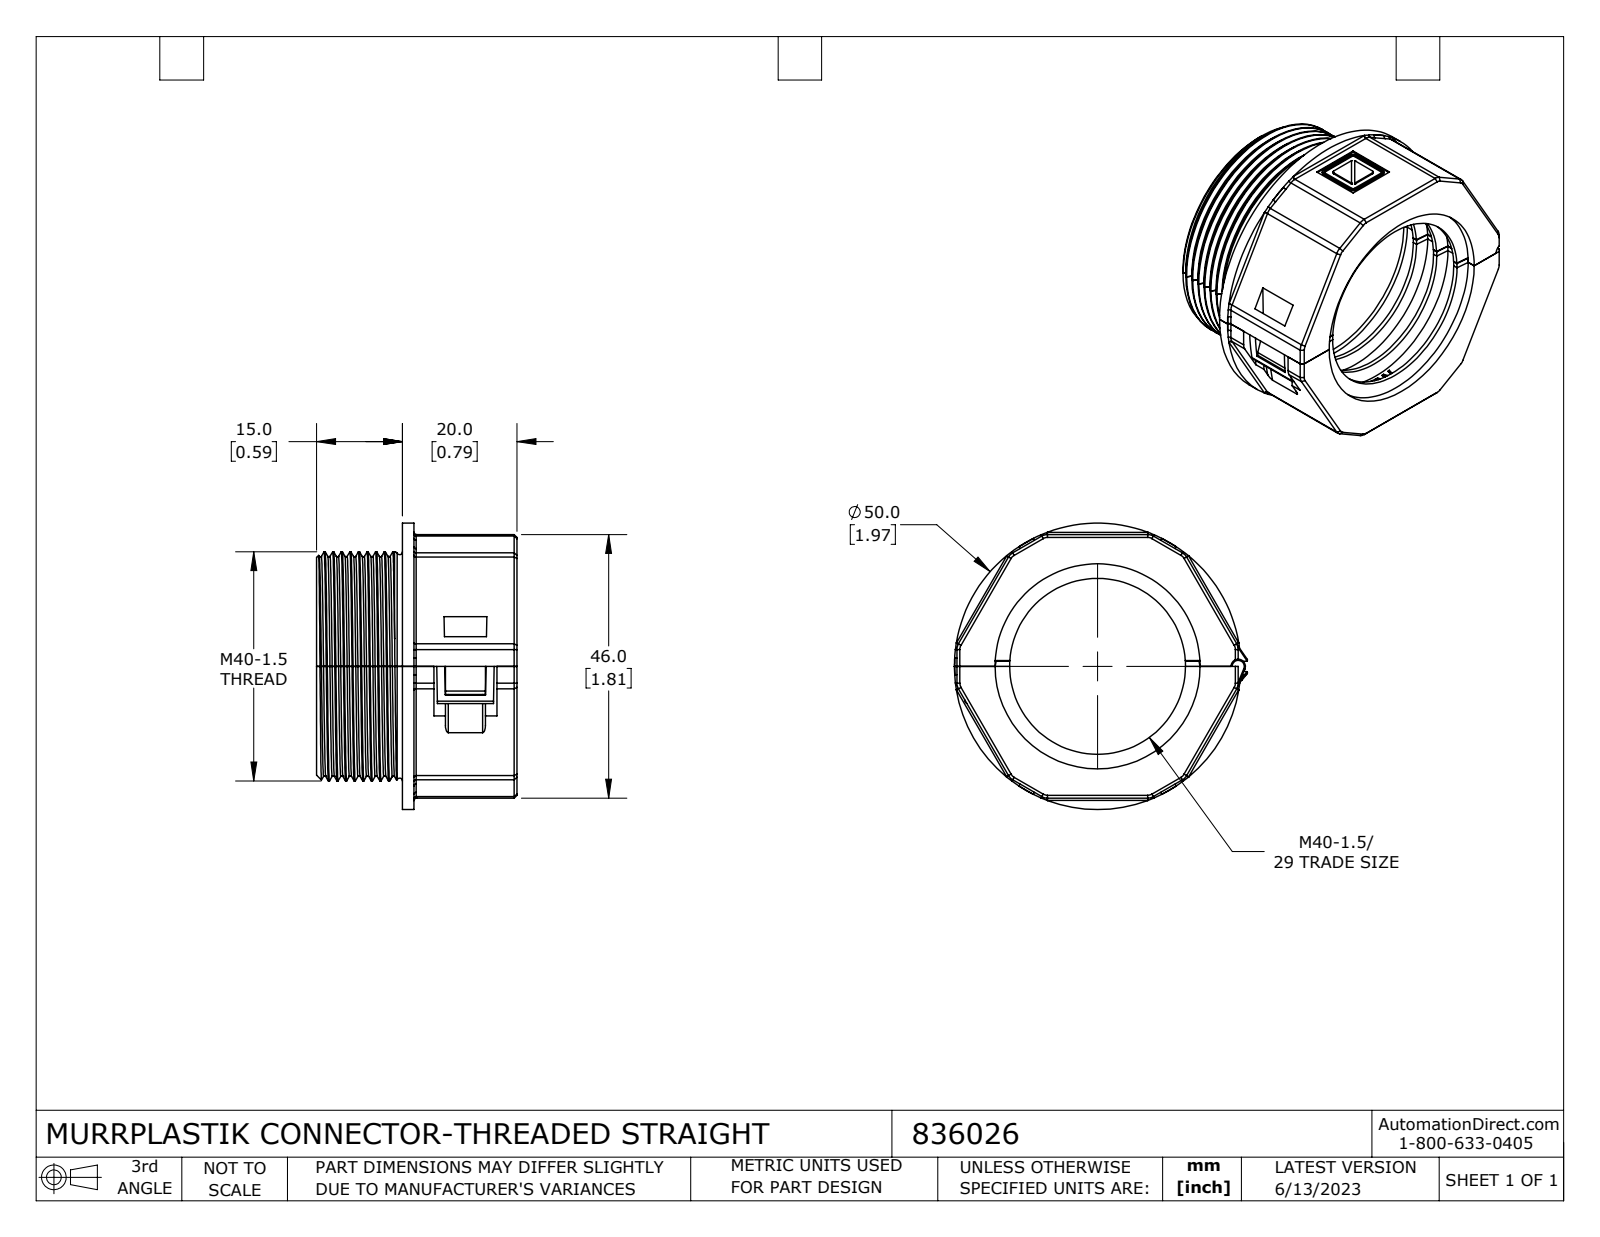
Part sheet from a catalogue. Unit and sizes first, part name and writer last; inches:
Units: inches
Overall size (bounding box): 2.015 × 1.969 × 1.378
Round holes (diameter × count): ⌀0.098 ×1, ⌀0.197 ×1, ⌀1.209 ×1, ⌀1.378 ×1, ⌀1.409 ×1
Round bosses / shafts (diameter × count): ⌀1.969 ×1, ⌀1.575 ×1
Partial cylindrical surfaces — rounded edges, fillets, slot ends (radius × count): R0.008 ×28, R0.016 ×16, R0.079 ×15, R0.02 ×9, R0.013 ×4, R0.025 ×4, R0.012 ×2, R0.039 ×2
Main face-to-face distances: 1.811, 0.787, 0.906, 1.934, 0.039, 0.079, 1.378, 0.591, 0.709, 0.669
Hole centre spacings: 0.967
Volume: 1.236 in³ · Surface area: 22.5 in²
Bodies: 2 solids, 767 faces (357 planar, 168 cylindrical, 242 other)
Part name (STEP PRODUCT): 836026
STEP written by: SolidWorks 2021 (CONFIG_CONTROL_DESIGN)
